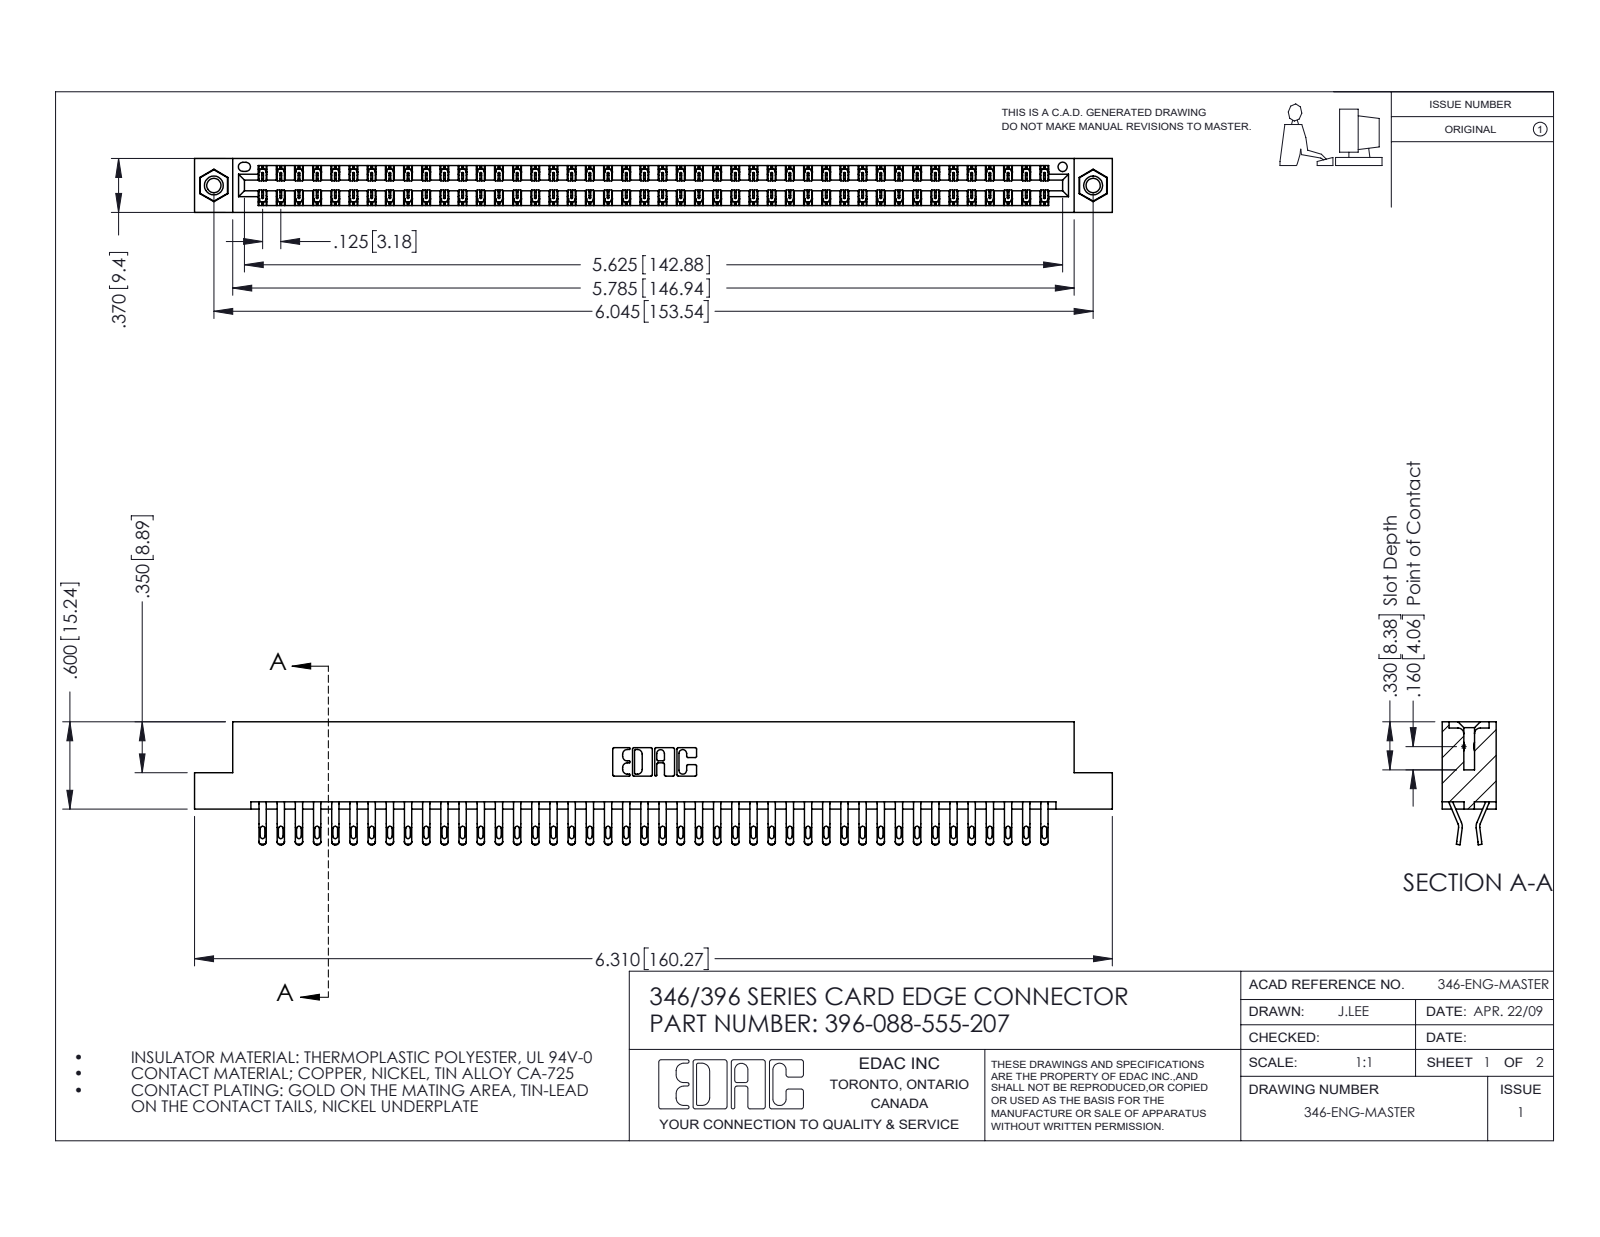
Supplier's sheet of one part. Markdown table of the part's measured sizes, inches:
| quantity | value |
| --- | --- |
| part name | 346 Part_Flush Mounting Lugs - 0.156 Dia-TI; 345-250-001_345-250-005-103; 345-292-001_555 Tail; 396-088-555-207 |
| STEP written by | SolidWorks 2016 (CONFIG_CONTROL_DESIGN) |
| units | inches |
| bodies | 91 solids, 5286 faces (3012 planar, 2258 cylindrical, 16 other) |
| overall size | 6.31 × 0.845 × 0.37 |
| volume | 0.969 in³ |
| surface area | 35.36 in² |
| round holes (diameter × count) | 0.098 × 2, 0.125 × 2, 0.156 × 2, 0.064 × 1 |
| round bosses / shafts (diameter × count) | 0.155 × 2 |
| partial cylindrical surfaces (radius × count) | 0.016 × 176, 0.02 × 176, 0.006 × 132, 0.01 × 22, 0.007 × 6, 0.031 × 6, 0.026 × 3, 0.01 × 2 |
| main face-to-face distances | 0.048, 0.322, 0.37, 0.25, 0.025, 0.072, 0.298, 0.275, 0.148, 0.222 |
| hole center spacings | 0.246, 5.836, 6.045 |
